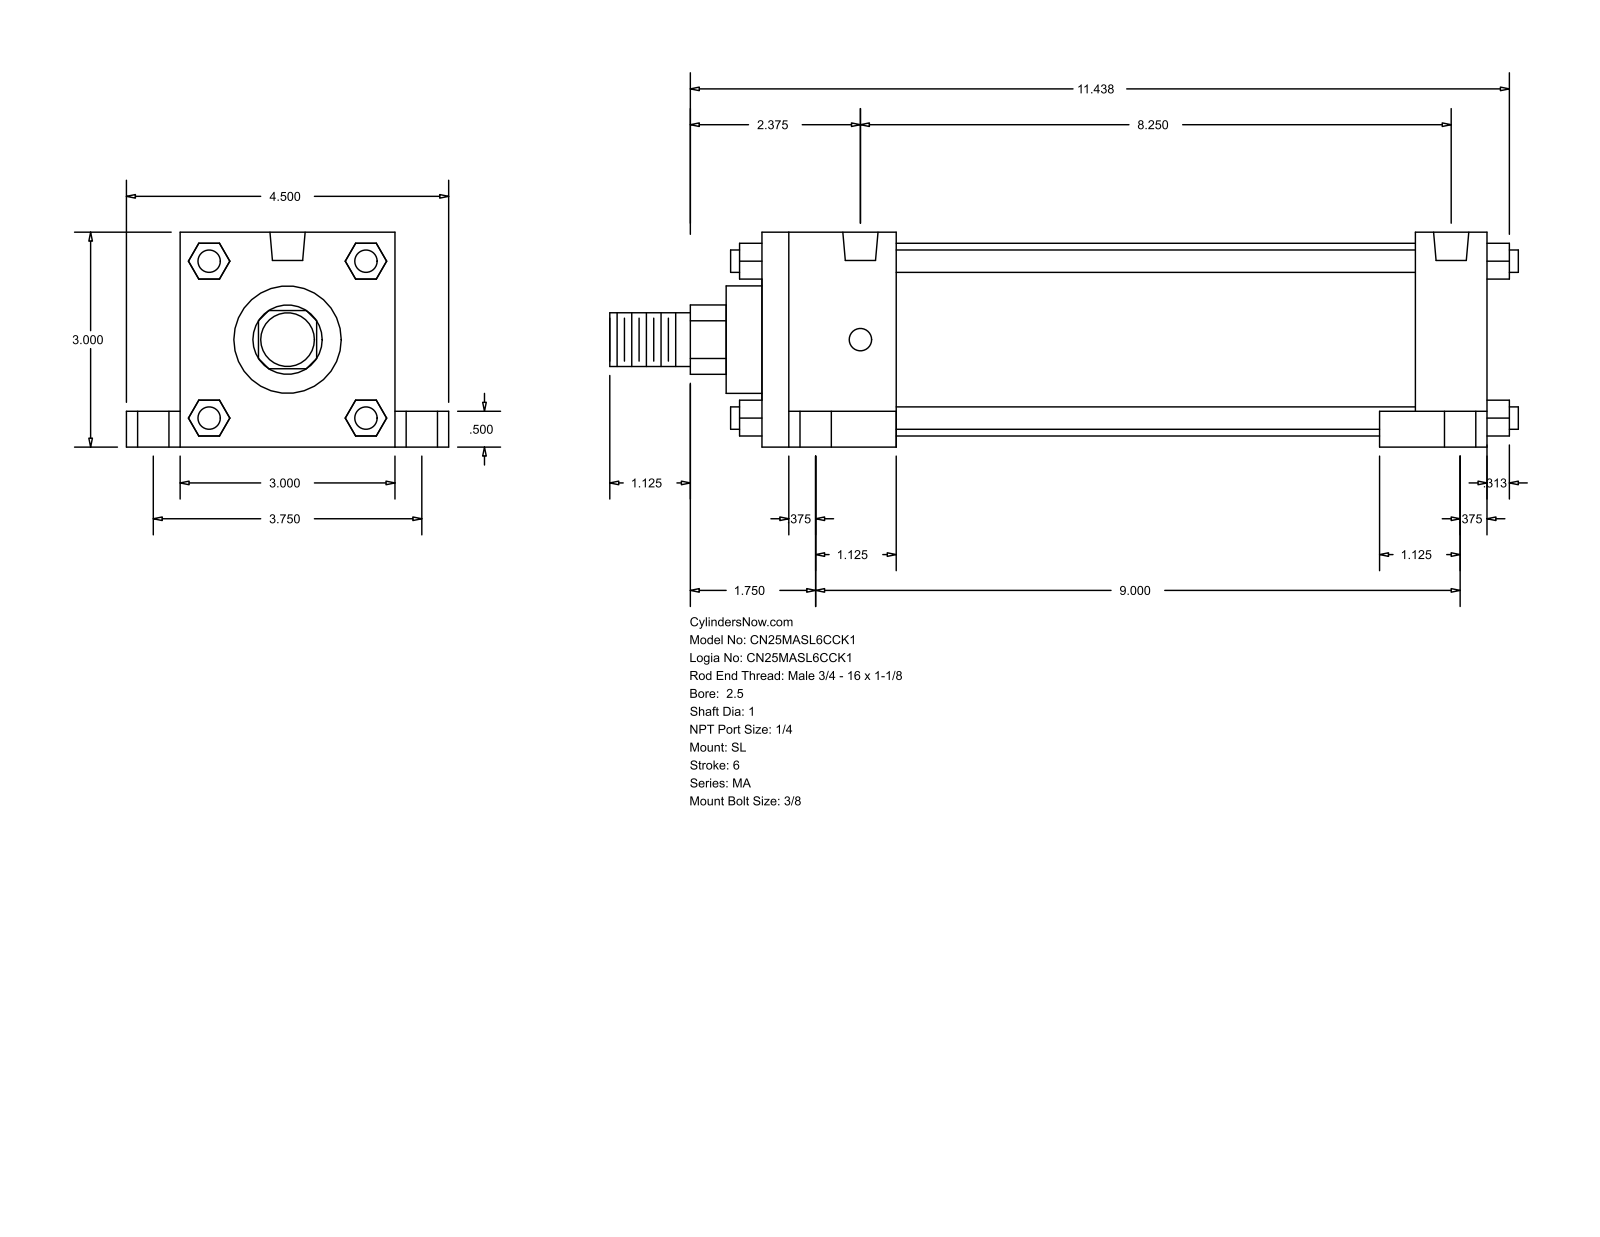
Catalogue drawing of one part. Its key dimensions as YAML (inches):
part_name: "MA_SL__0250_1"
step_written_by: "GSSL Pune (CONFIG_CONTROL_DESIGN)"
units: inches
bodies: {solids: 0, faces: 148, planar: 112, cylindrical: 36, other: 0}
overall_size: [12.687, 4.5, 3]
round_holes:
  - {diameter: 0.313, count: 4}
  - {diameter: 0.437, count: 4}
  - {diameter: 0.687, count: 4}
  - {diameter: 0.492, count: 2}
round_bosses_or_shafts:
  - {diameter: 0.313, count: 4}
  - {diameter: 2.69, count: 1}
  - {diameter: 1.5, count: 1}
  - {diameter: 1, count: 1}
  - {diameter: 0.75, count: 1}
partial_cylinders:
  - {radius: 0.484, count: 1}
face_to_face_distances: [3, 10.125, 0.5, 7.25, 1, 1.875, 8.25, 9.125, 0.75, 3.75]
hole_center_spacings: [1.879, 1.976, 3.75, 8.25, 8.582, 9, 9.071, 9.75]
